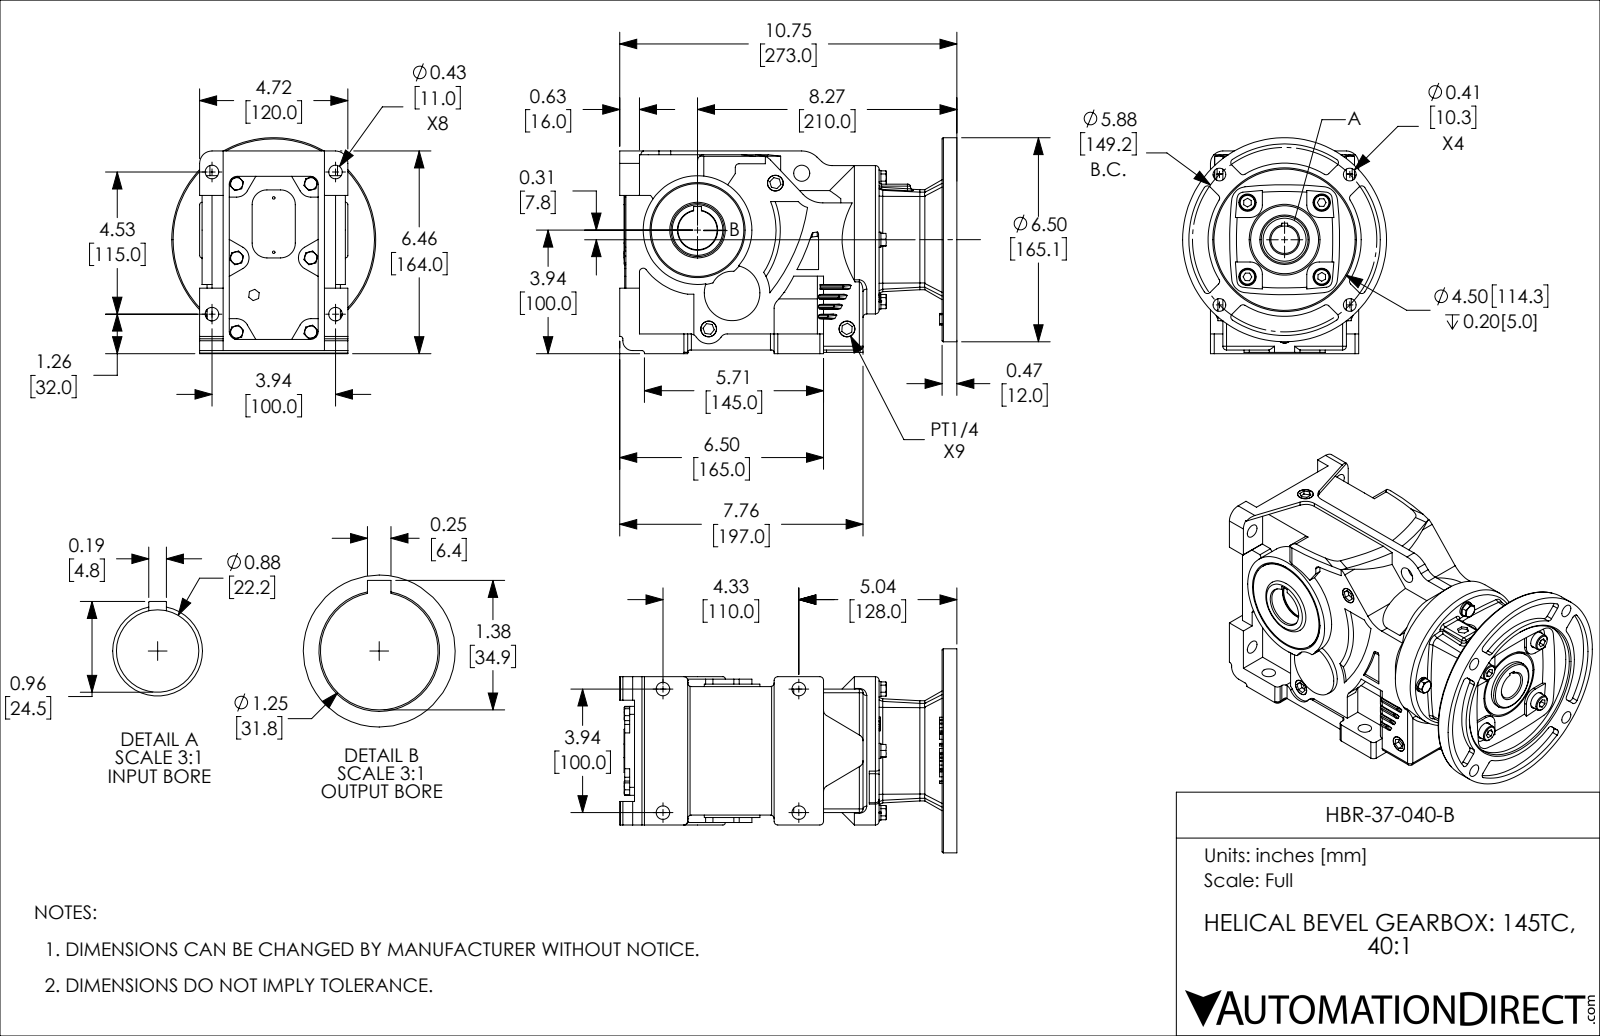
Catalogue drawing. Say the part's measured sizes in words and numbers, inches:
The part is named "HBR-37-040-B". Its 3-D file was written by "SolidWorks 2018 (AUTOMOTIVE_DESIGN)". It is 1 solid with 1103 faces: 542 planar, 292 cylindrical and 269 other. Overall it measures 10.748 by 6.88 by 6.5 inches. Its volume is 210.9 cubic inches and its surface area 395.6 square inches. Round holes: 8 of diameter 0.433, 4 of diameter 0.24, 4 of diameter 0.276, 4 of diameter 0.406, 4 of diameter 0.551, 2 of diameter 0.079, 1 of diameter 0.512, 1 of diameter 0.875, 1 of diameter 1.25, 1 of diameter 1.327, 1 of diameter 4.5. Round bosses or shafts: 4 of diameter 0.512, 4 of diameter 0.48, 4 of diameter 0.236, 1 of diameter 6.5, 1 of diameter 4.724, 1 of diameter 3.465, 1 of diameter 2.953, 1 of diameter 2.165. Partial cylindrical surfaces (rounded edges, fillets, slot ends): 38 of radius 0.118, 18 of radius 0.039, 14 of radius 0.394, 11 of radius 0.197, 10 of radius 0.079, 6 of radius 0.472, 4 of radius 0.157, 4 of radius 0.256. The main face-to-face distances are 0.472, 0.315, 0.118, 0.157, 0.079, 4.252, 0.276, 0.394, 3.937, 0.512. The hole center spacings are 2.08, 4.548, 3.937, 1.42, 1.673, 1.969, 2.784, 2.937.
